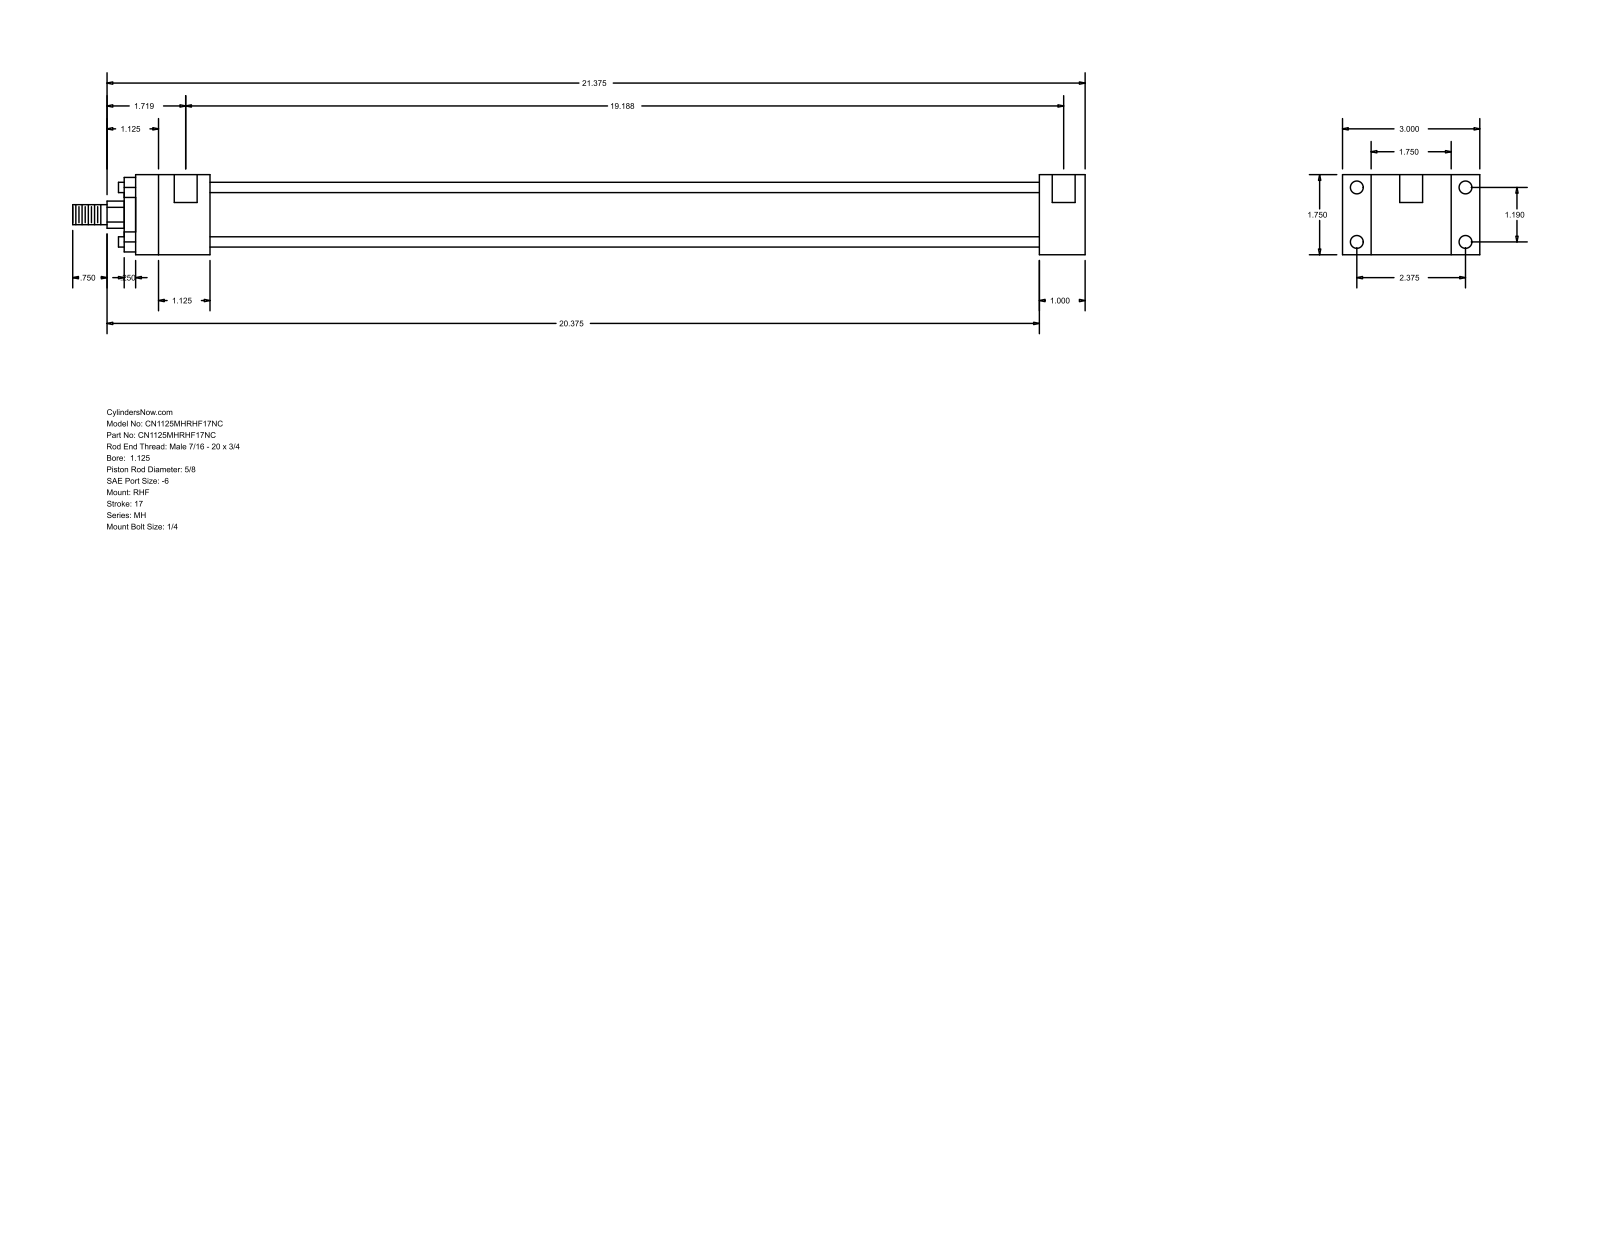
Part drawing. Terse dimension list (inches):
name: MH_RHF__0112_0.625
written by: GSSL Pune (CONFIG_CONTROL_DESIGN)
unit: in
bodies: 0 solids, 88 faces (60 planar, 28 cylindrical, 0 other)
size: 22.125 × 3 × 1.75
holes: 4× ⌀0.219, 4× ⌀0.281, 2× ⌀0.5
bosses: 4× ⌀0.225, 1× ⌀1.375, 1× ⌀1.125, 1× ⌀0.625, 1× ⌀0.437
rounds: 1× R0.297
face distances: 1.75, 0.625, 1, 2.375, 3, 18.125, 19.125, 1.625, 19.75, 20.75
hole spacings: 1.19, 2.375, 2.656, 19.063, 0.125, 19.187
